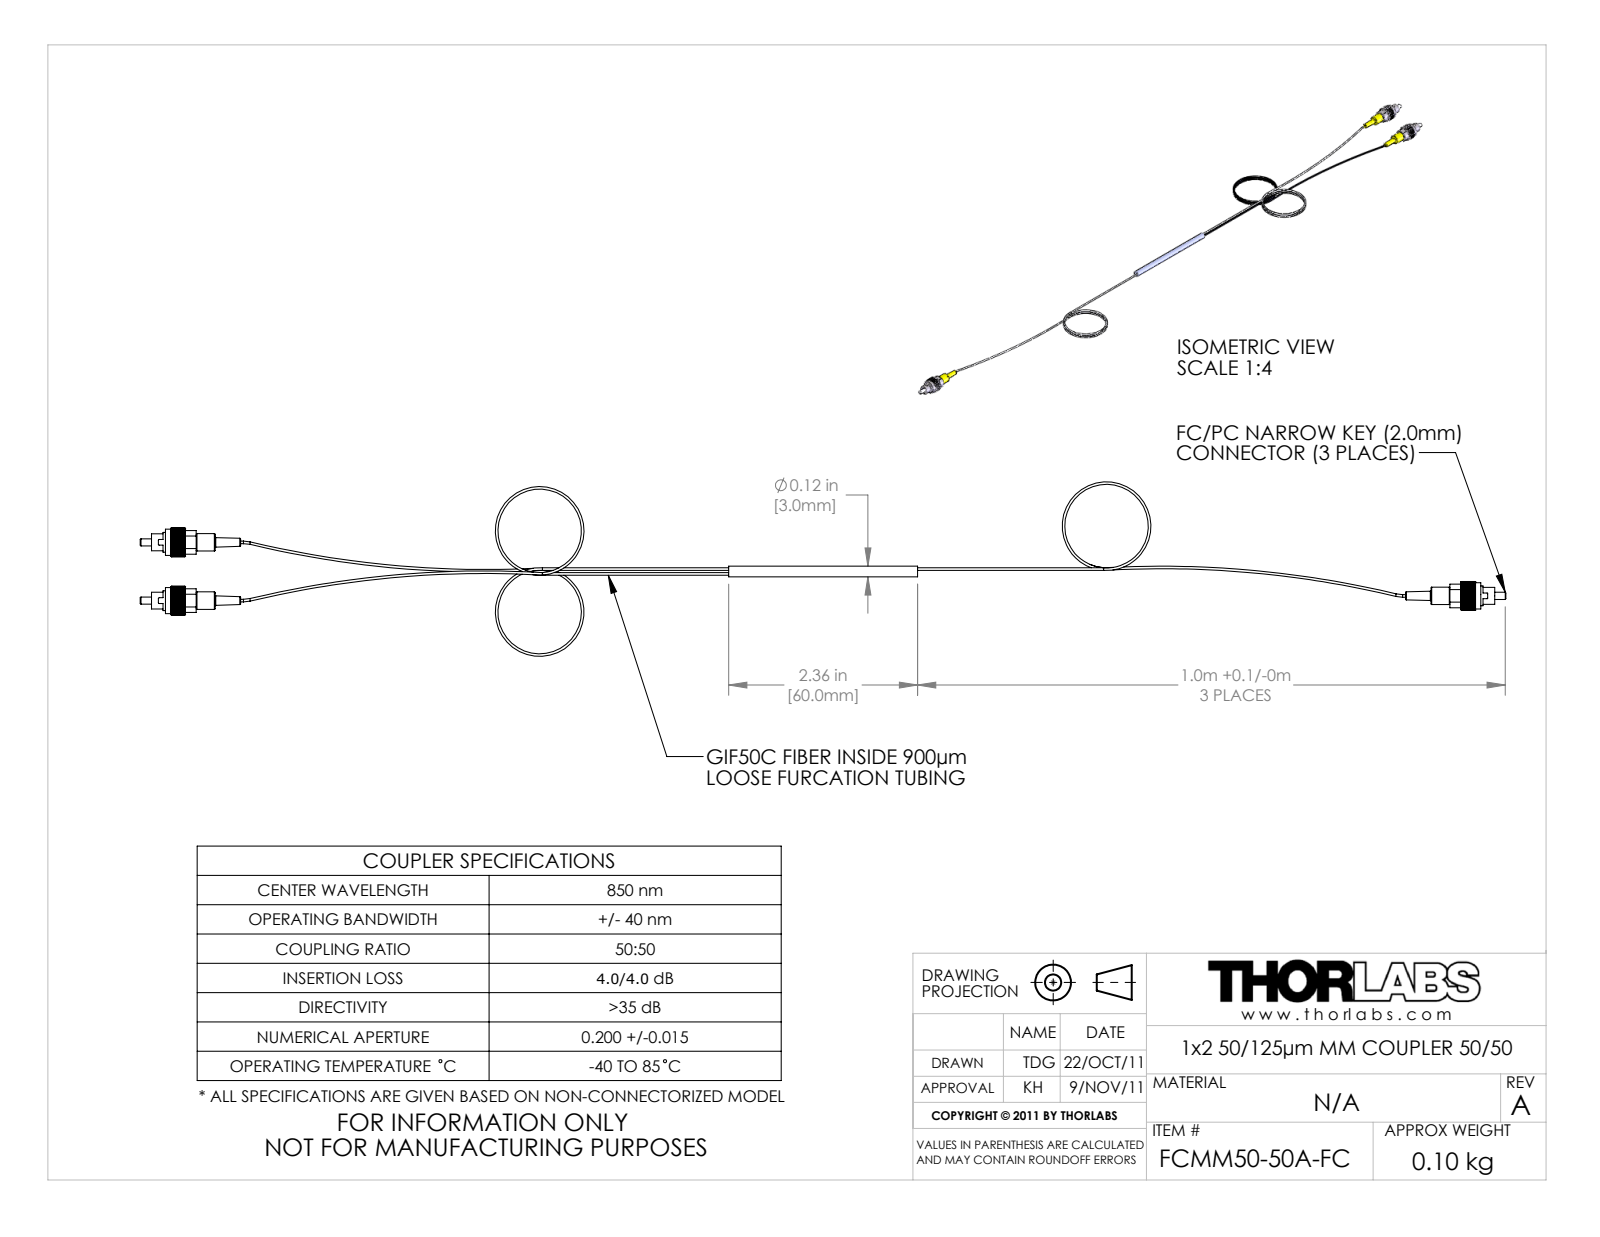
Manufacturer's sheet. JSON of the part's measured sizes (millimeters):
{"part_name": "13896-E0W", "step_written_by": "SolidWorks 2011 (AUTOMOTIVE_DESIGN)", "units": "millimeters", "bodies": {"solids": 13, "faces": 904, "planar": 460, "cylindrical": 348, "other": 96}, "overall_size": [477, 61, 16], "volume_mm3": 3740, "surface_area_mm2": 10900, "round_holes": [[1.4, 3], [4.9, 3], [5.3, 3], [6.4, 3], [6.9, 3], [9.1, 3], [1, 2], [8.3, 2], [3.3, 1], [8.3, 1]], "round_bosses_or_shafts": [[0.9, 5], [6.9, 3], [6.1, 3], [5.9, 3], [4.8, 3], [4, 3], [3.6, 3], [2.5, 3]], "partial_cylinders_radius": [[0.3, 6], [5, 3], [4.1, 2], [4.1, 1]], "face_to_face_distances": [6.8, 6.8, 2.9, 6.7, 3.7, 0.8, 13, 10.1, 6.4, 448.3], "hole_center_spacings": [9.8, 0.8, 10.6, 11.4, 1.7, 6.2, 8.3, 9]}
